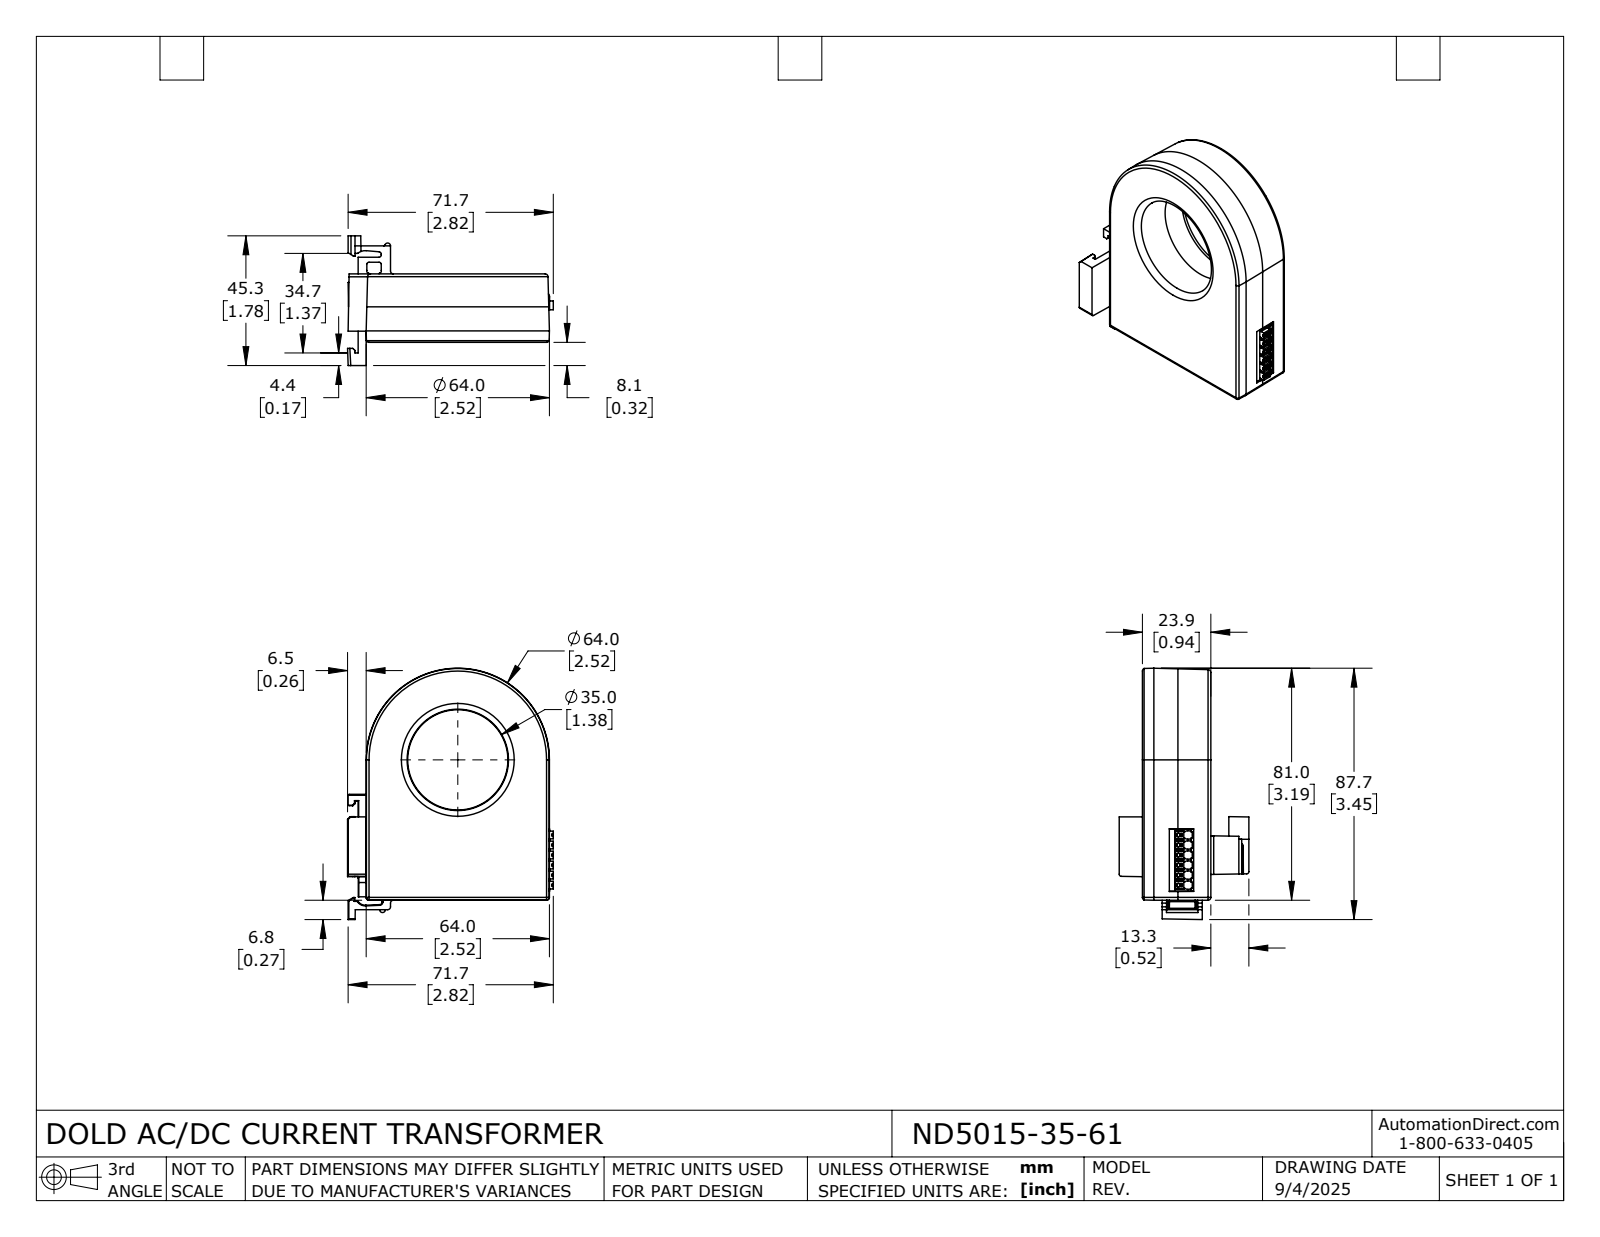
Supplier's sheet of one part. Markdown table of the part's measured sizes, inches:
| quantity | value |
| --- | --- |
| part name | ND5015-035-61 |
| STEP written by | SolidWorks 2024 (AUTOMOTIVE_DESIGN) |
| units | inches |
| bodies | 1 solid, 387 faces (271 planar, 69 cylindrical, 47 other) |
| overall size | 3.455 × 2.829 × 1.783 |
| volume | 5.742 in³ |
| surface area | 30.63 in² |
| round holes (diameter × count) | 0.047 × 6 |
| partial cylindrical surfaces (radius × count) | 0.039 × 17, 0.071 × 12, 0.02 × 11, 0.03 × 3, 0.01 × 2, 0.021 × 1, 0.059 × 1, 0.079 × 1 |
| main face-to-face distances | 0.941, 2.52, 0.138, 0.11, 0.445, 0.385, 1.326, 0.13, 0.319, 1.645 |
| hole center spacings | 0.138, 0.276, 0.413, 0.551, 0.689 |
